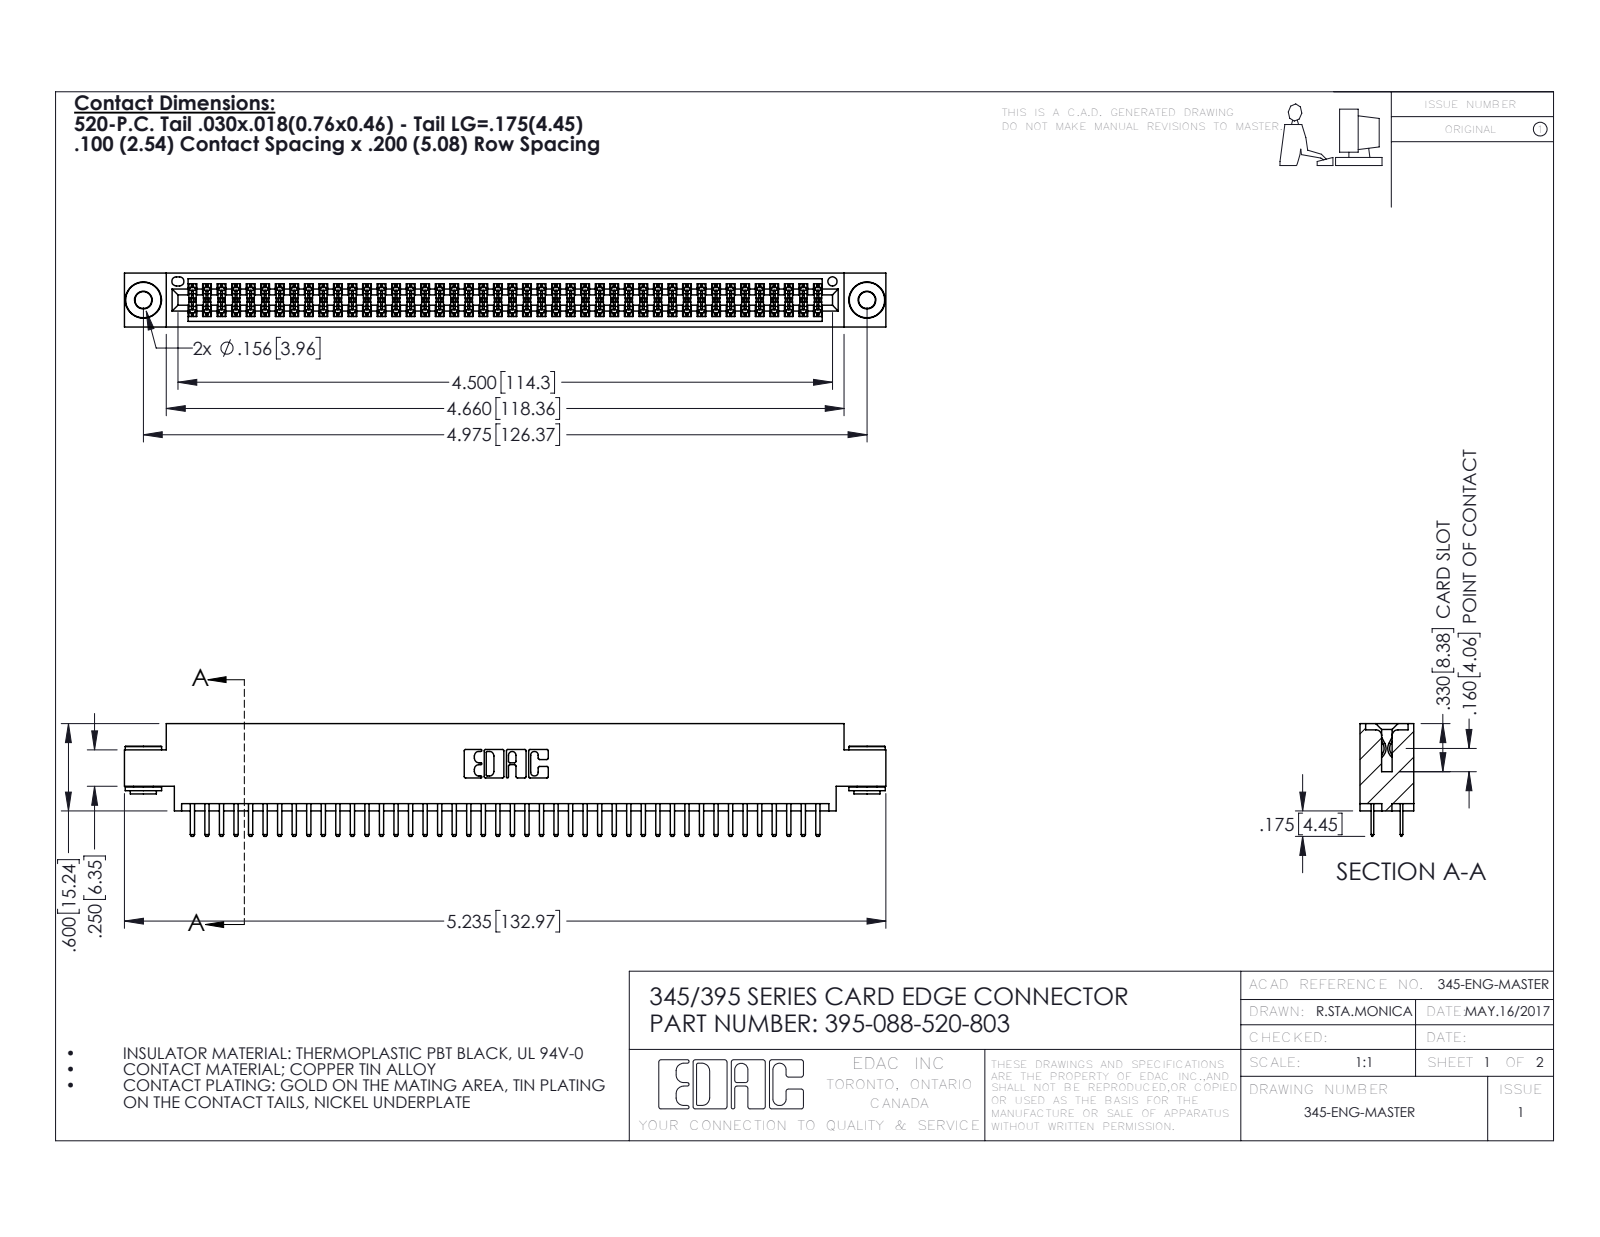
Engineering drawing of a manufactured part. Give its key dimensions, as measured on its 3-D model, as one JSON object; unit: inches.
{"part_name": "395-088-520-803; 345 Part_0.170 Offset - 0.156 Dia-TH; 345-250-002_345-250-002-102; 345-292-001_345-293-120", "step_written_by": "SolidWorks 2016 (CONFIG_CONTROL_DESIGN)", "units": "inches", "bodies": {"solids": 91, "faces": 4920, "planar": 3174, "cylindrical": 1738, "other": 8}, "overall_size": [5.235, 0.775, 0.37], "volume_in3": 0.781, "surface_area_in2": 29.81, "round_holes": [[0.116, 2], [0.156, 2], [0.064, 1]], "round_bosses_or_shafts": [[0.25, 2], [0.18, 2], [0.136, 2]], "partial_cylinders_radius": [[0.006, 132], [0.01, 92], [0.01, 22], [0.007, 6], [0.031, 6], [0.026, 3], [0.014, 2], [0.019, 2]], "face_to_face_distances": [0.072, 0.298, 0.2, 0.37, 0.098, 0.272, 0.025, 0.225, 0.175, 0.022], "hole_center_spacings": [0.27, 4.739, 4.975]}
